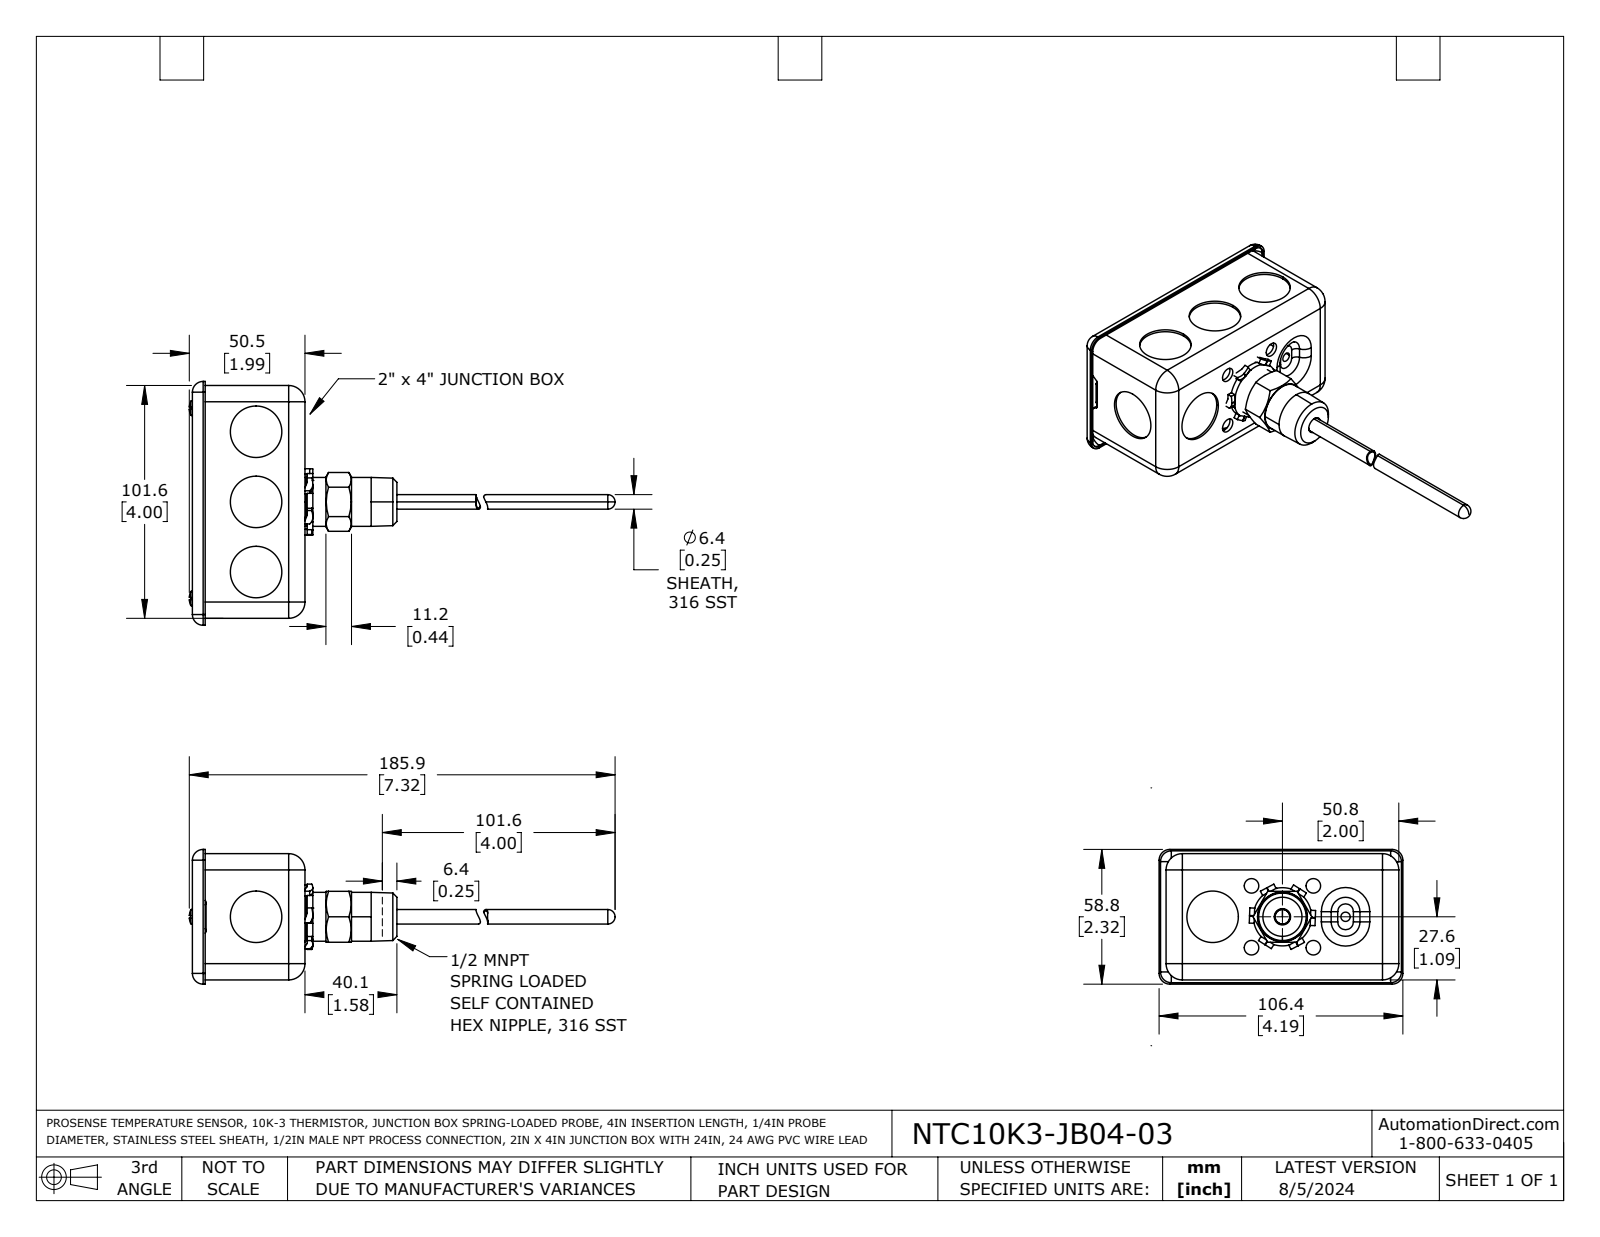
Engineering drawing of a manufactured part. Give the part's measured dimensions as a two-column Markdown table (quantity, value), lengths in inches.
| quantity | value |
| --- | --- |
| part name | NTC10K3-JB04-03 |
| STEP written by | SolidWorks 2021 (AUTOMOTIVE_DESIGN) |
| units | inches |
| bodies | 5 solids, 366 faces (155 planar, 147 cylindrical, 64 other) |
| overall size | 7.313 × 4.19 × 2.315 |
| volume | 3.078 in³ |
| surface area | 98.43 in² |
| round holes (diameter × count) | 0.885 × 6, 0.25 × 4, 0.115 × 2, 0.16 × 1, 0.21 × 1, 0.26 × 1, 0.438 × 1, 0.466 × 1 |
| round bosses / shafts (diameter × count) | 0.136 × 2, 0.84 × 1, 0.25 × 1 |
| partial cylindrical surfaces (radius × count) | 0.185 × 16, 0.245 × 8, 0.28 × 8, 0.174 × 6, 0.555 × 6, 0.045 × 4, 0.165 × 4, 0.07 × 2 |
| main face-to-face distances | 0.07, 0.03, 2.03, 2.1, 0.04, 0.1, 0.06, 1.855, 2.07, 2 |
| hole center spacings | 0.751, 1.062, 1.248, 2.254, 0.767, 0.854, 1.205, 1.502 |
